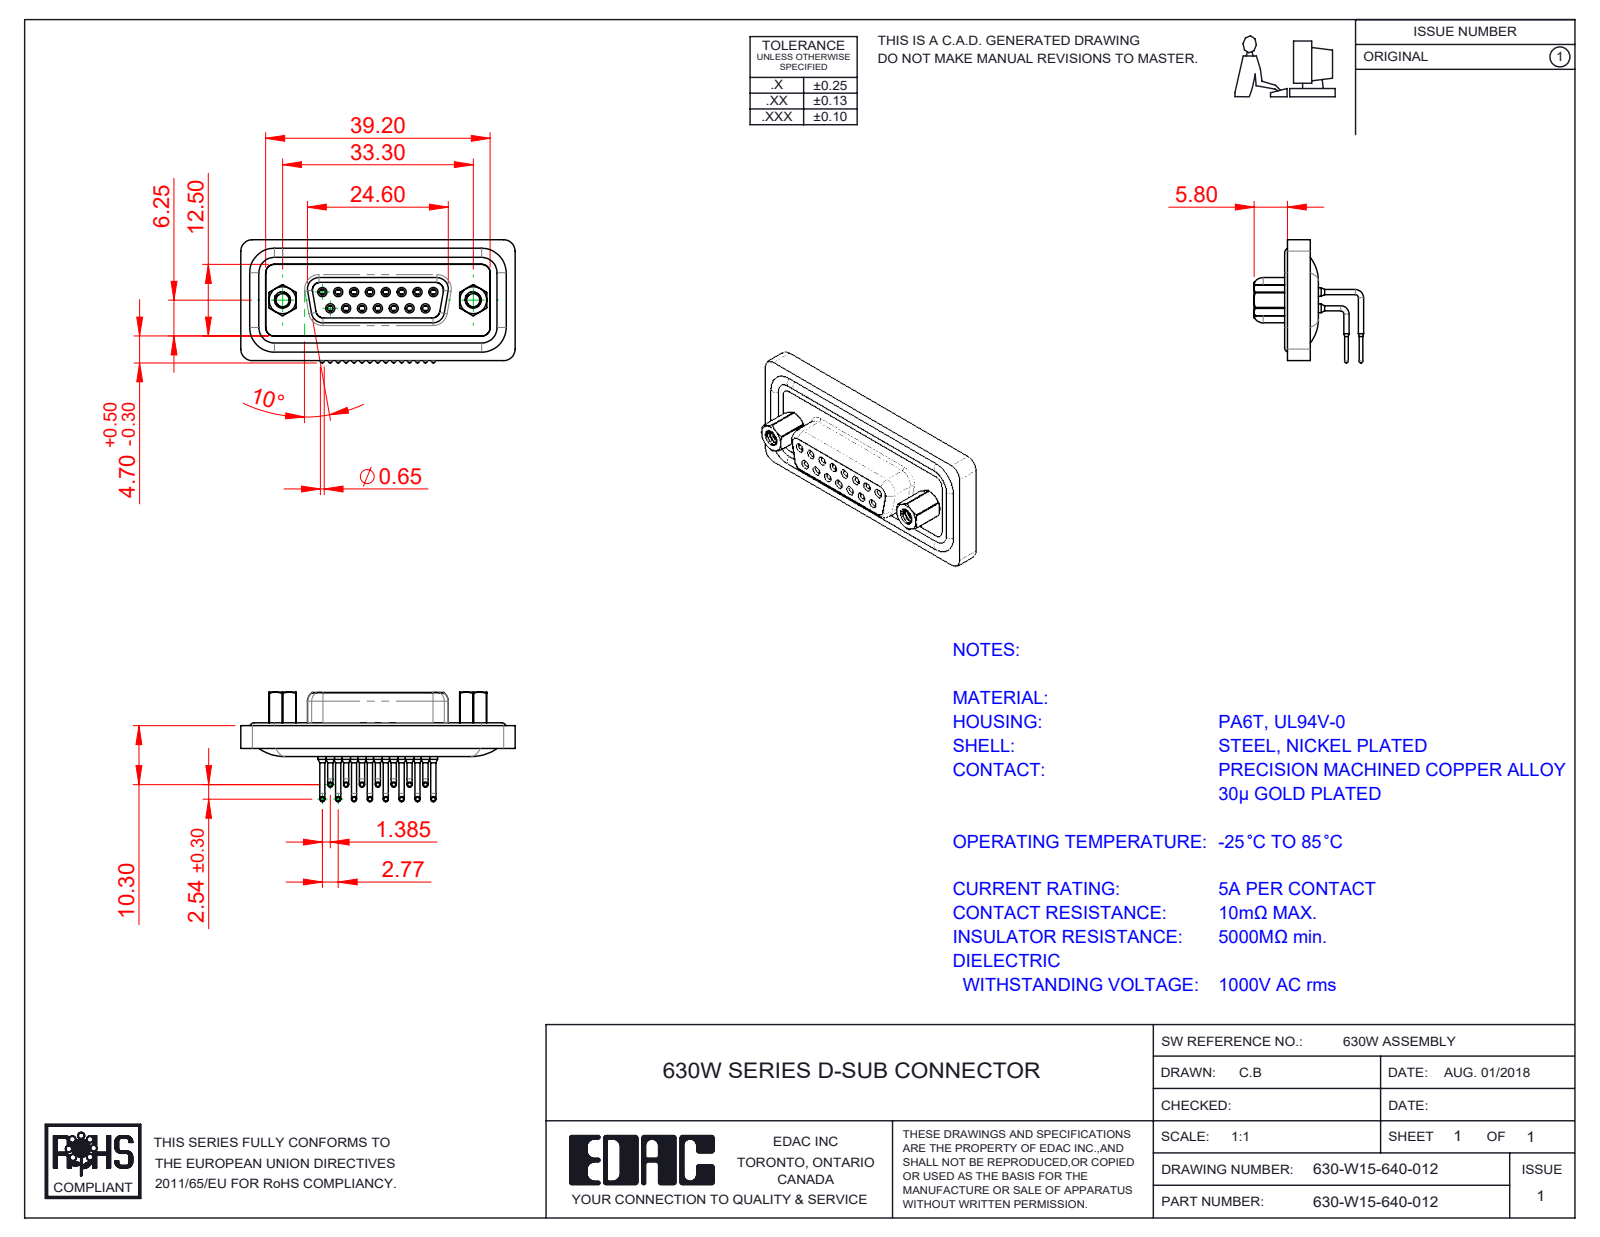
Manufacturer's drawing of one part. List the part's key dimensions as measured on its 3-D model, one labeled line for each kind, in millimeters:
Part name (STEP PRODUCT): 630W 4-40 Threaded Rivet_Stabilizer; 630-W15-640-012; 630W Housing_15 Contacts; 630W 4-40 Hex Standoff (+4 more)
STEP written by: SolidWorks 2023 (CONFIG_CONTROL_DESIGN)
Units: millimetres
Bodies: 23 solids, 1242 faces (326 planar, 591 cylindrical, 325 other)
Overall size (bounding box): 47.89 × 21.5 × 19.59
Volume: 5 547 mm³ · Surface area: 9 683 mm²
Round holes (diameter × count): ⌀1 ×15, ⌀1.1 ×15, ⌀1.5 ×15, ⌀1.7 ×15, ⌀1.8 ×15, ⌀2 ×15, ⌀2.26 ×2, ⌀2.29 ×2, ⌀4 ×2, ⌀4.8 ×2, ⌀5 ×2
Round bosses / shafts (diameter × count): ⌀0.9 ×30, ⌀1.6 ×19, ⌀1.5 ×15, ⌀0.65 ×15, ⌀4.9 ×2, ⌀2.79 ×2, ⌀5 ×1
Partial cylindrical surfaces — rounded edges, fillets, slot ends (radius × count): R2 ×16, R1.5 ×14, R1.35 ×8, R2.7 ×6, R0.5 ×4, R0.9 ×4, R1.6 ×4, R1.75 ×4
Main face-to-face distances: 0.4, 1.8, 1.6, 1.1, 2.5, 2.9, 0.5, 9.8, 4.5, 7.45
Hole centre spacings: 3.16, 2.77, 5.54, 8.31, 3.17, 3.15, 11.08, 5.03
